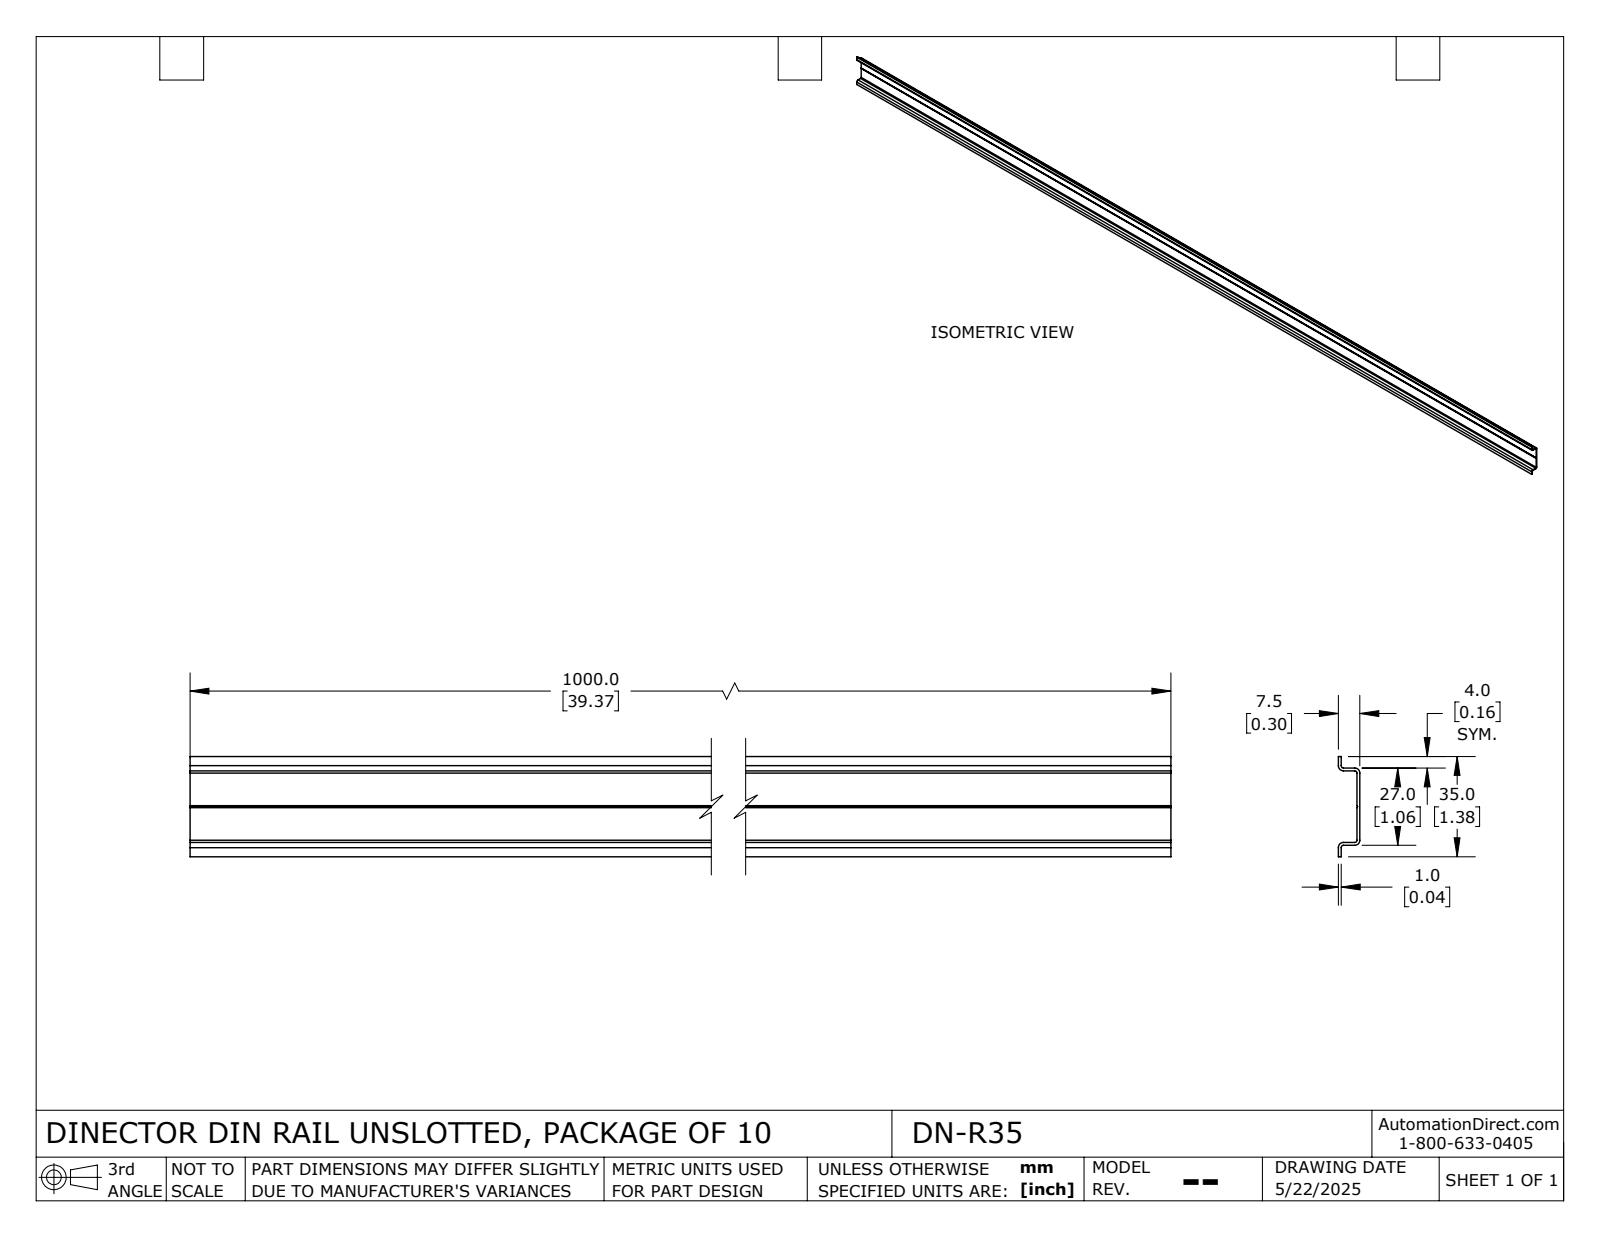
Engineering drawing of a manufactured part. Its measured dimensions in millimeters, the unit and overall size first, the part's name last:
Units: millimetres
Overall size (bounding box): 1000 × 35 × 7.5
Partial cylindrical surfaces — rounded edges, fillets, slot ends (radius × count): R0.8 ×4, R1.8 ×4
Main face-to-face distances: 1, 6.5, 26, 5.5, 7.5, 27, 25, 4, 5, 30
Volume: 45 699 mm³ · Surface area: 93 735 mm²
Bodies: 1 solid, 25 faces (17 planar, 8 cylindrical, 0 other)
Part name (STEP PRODUCT): DN-R35S_Default
STEP written by: SolidWorks 2024 (CONFIG_CONTROL_DESIGN)
